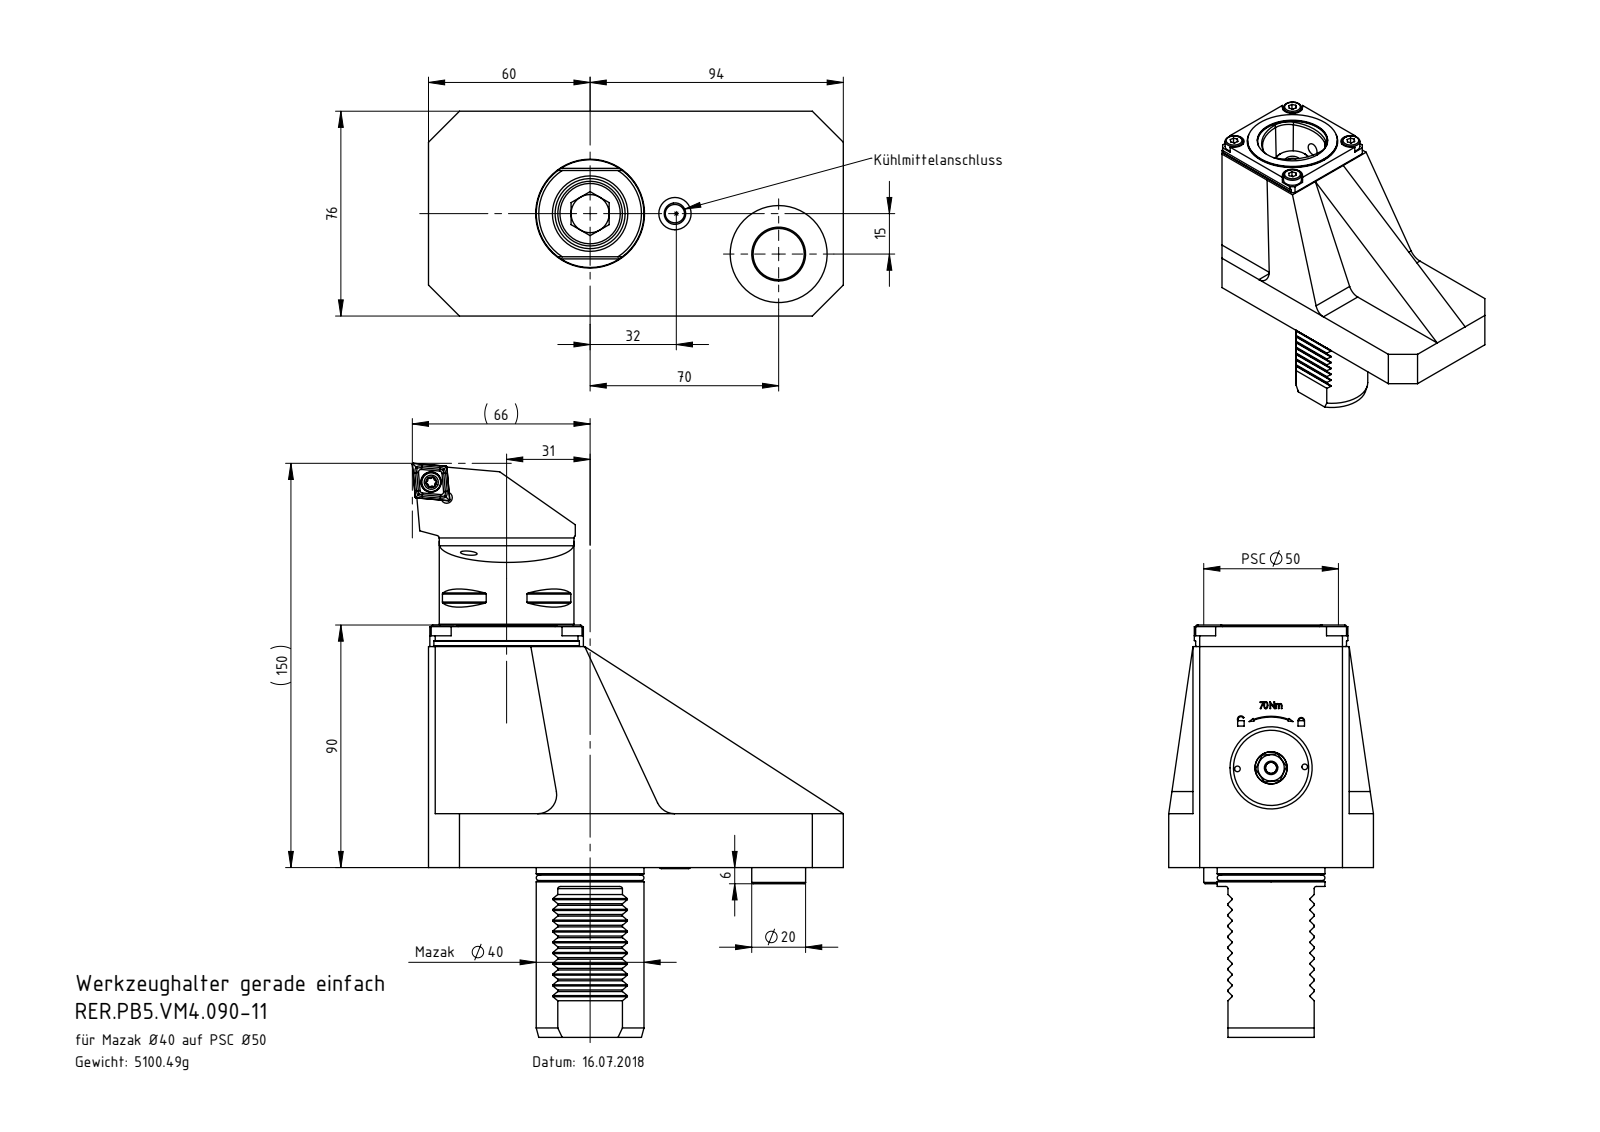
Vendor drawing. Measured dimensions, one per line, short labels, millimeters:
name: ISO 4762 - M4 x 40-12.9_PreviewCfg; ISO 8734 - 5 x 12_PreviewCfg; VD4-ER1.040.066_abgefräst; 777.18513.002.1.01.01.01 (+8 more)
written by: SolidWorks 2017 (AUTOMOTIVE_DESIGN)
unit: mm
bodies: 34 solids, 958 faces (415 planar, 227 cylindrical, 316 other)
size: 154 × 153 × 76
volume: 600 721 mm³; area: 139 434 mm²
holes: 5× ⌀5, 4× ⌀4.2, 4× ⌀6.2, 3× ⌀2.1, 3× ⌀3, 2× ⌀3.3, 2× ⌀4.17, 2× ⌀6.8, 2× ⌀12, 2× ⌀26, 1× ⌀7, 1× ⌀7.1
bosses: 4× ⌀10, 4× ⌀6, 2× ⌀20, 2× ⌀7, 2× ⌀4, 1× ⌀50, 1× ⌀49.7, 1× ⌀46.5
rounds: 30× R0.3, 4× R5, 4× R5.6, 2× R0.2, 2× R0.8, 2× R4, 2× R4.05, 2× R4.1
face distances: 20, 9, 27, 67, 49, 40, 18, 58, 22, 62
hole spacings: 32.53, 46, 15.01, 20.5, 24.04, 24.35, 31.97, 43.98
